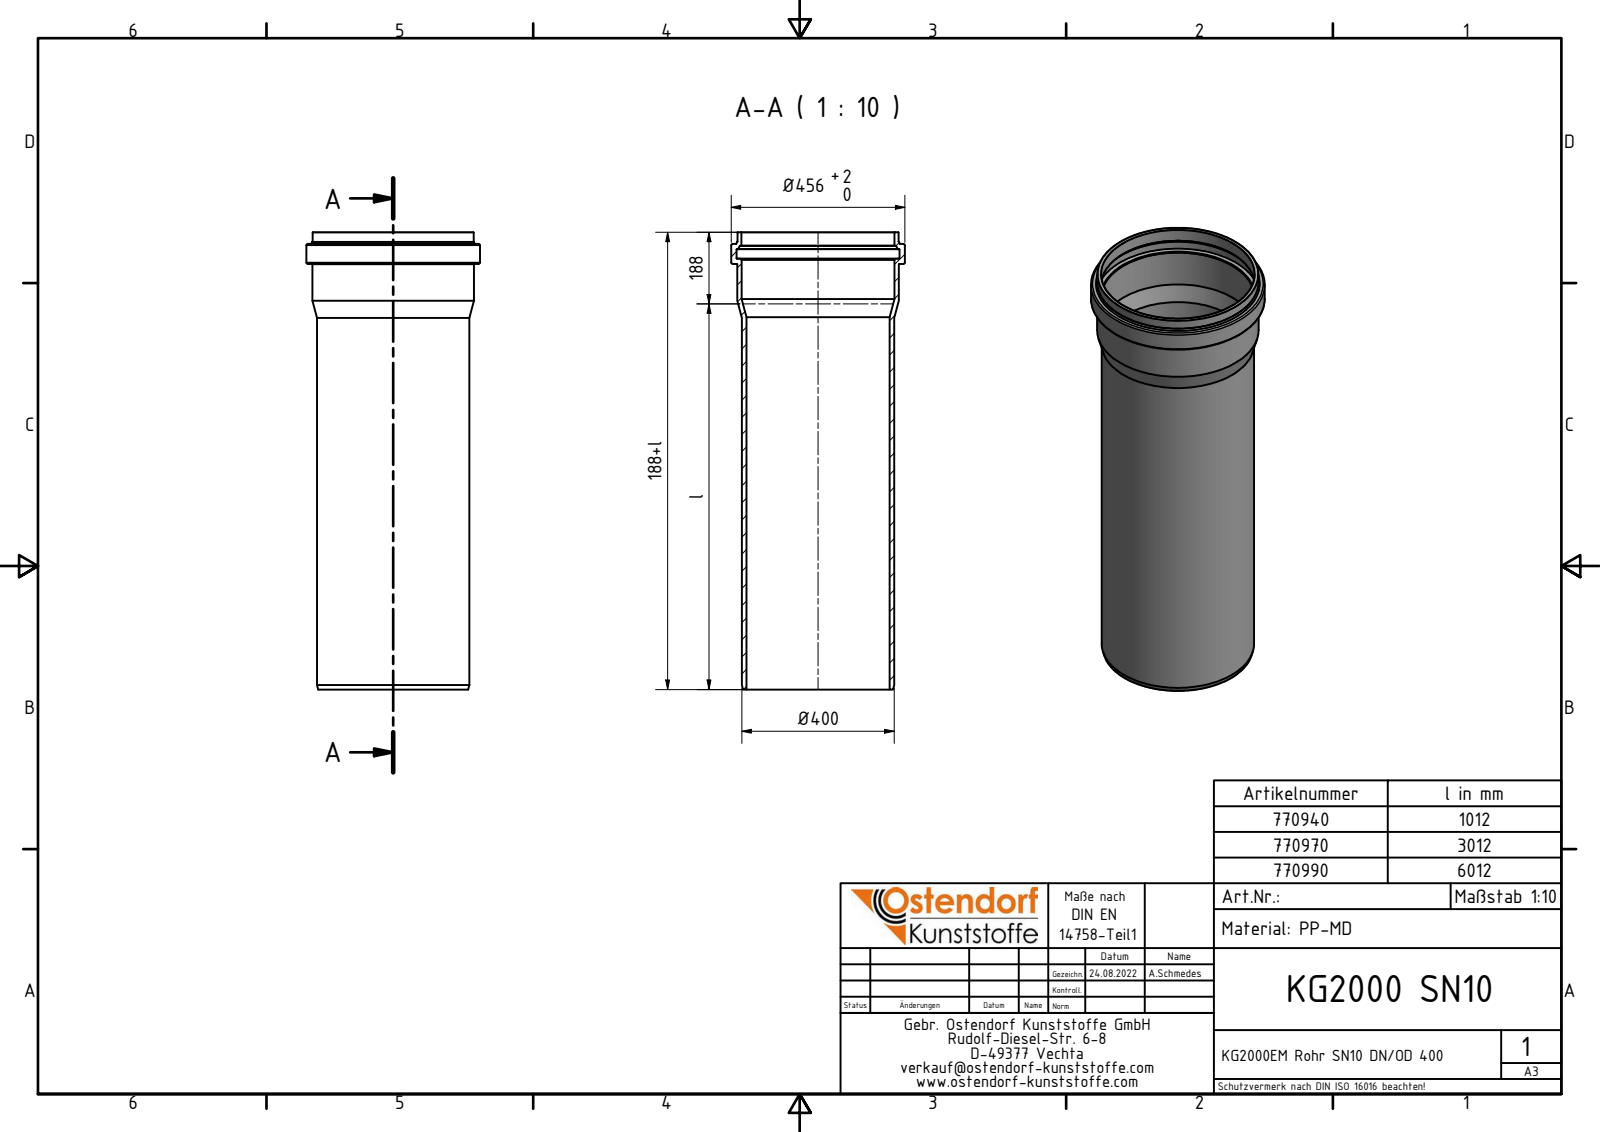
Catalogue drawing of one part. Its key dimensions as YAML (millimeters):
part_name: "770940 KG2000EM Rohr SN10 DN-OD 400x1000"
step_written_by: "Autodesk Inventor 2020 (AUTOMOTIVE_DESIGN)"
units: millimeters
bodies: {solids: 1, faces: 36, planar: 5, cylindrical: 9, other: 22}
overall_size: [1200, 456, 456]
volume: 18180000
surface_area: 3053000
round_holes:
  - {diameter: 376, count: 1}
  - {diameter: 401.7, count: 1}
  - {diameter: 402.1, count: 1}
  - {diameter: 427.7, count: 1}
round_bosses_or_shafts:
  - {diameter: 456, count: 1}
  - {diameter: 423.9, count: 1}
  - {diameter: 423.06, count: 1}
  - {diameter: 400, count: 1}
face_to_face_distances: [52.7, 83.25, 30.55, 1116.75, 1169.45, 1200, 1127.3, 10.55, 42.15, 72.7]
